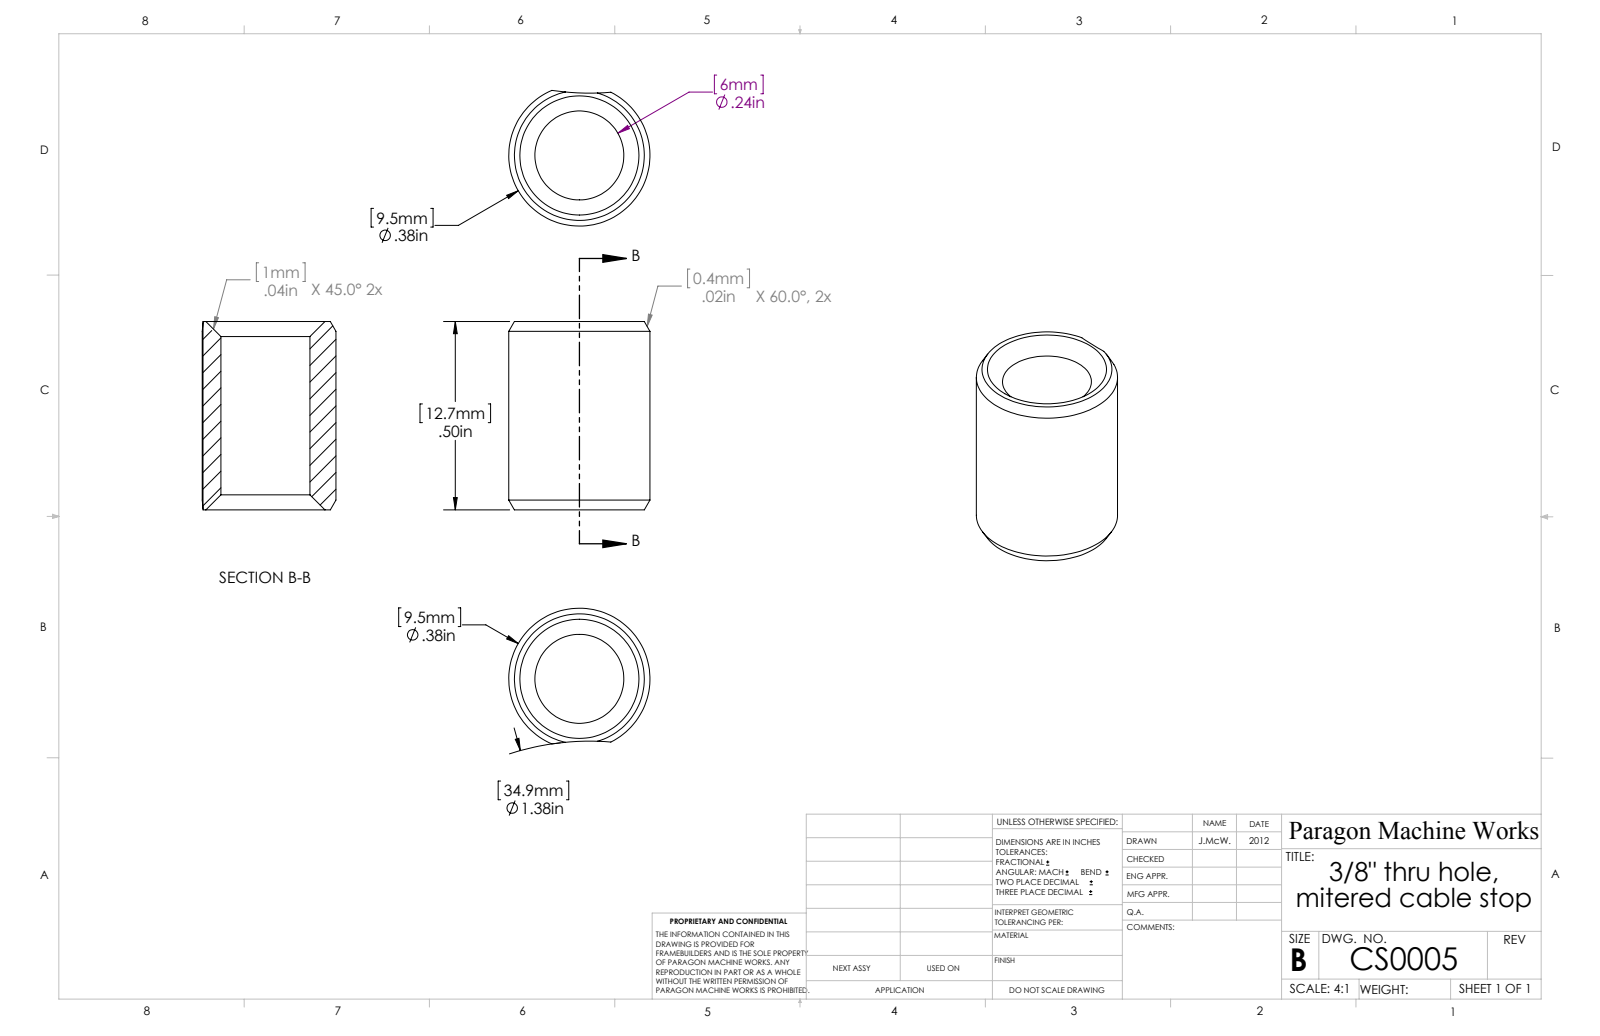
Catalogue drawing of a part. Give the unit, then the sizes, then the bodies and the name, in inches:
Units: inches
Overall size (bounding box): 0.5 × 0.375 × 0.36
Round holes (diameter × count): ⌀0.236 ×1
Round bosses / shafts (diameter × count): ⌀0.375 ×1
Partial cylindrical surfaces — rounded edges, fillets, slot ends (radius × count): R0.687 ×1
Main face-to-face distances: 0.5
Volume: 0.03 in³ · Surface area: 1.031 in²
Bodies: 1 solid, 13 faces (2 planar, 4 cylindrical, 7 other)
Part name (STEP PRODUCT): CS0005
STEP written by: SolidWorks 2023 (CONFIG_CONTROL_DESIGN)
